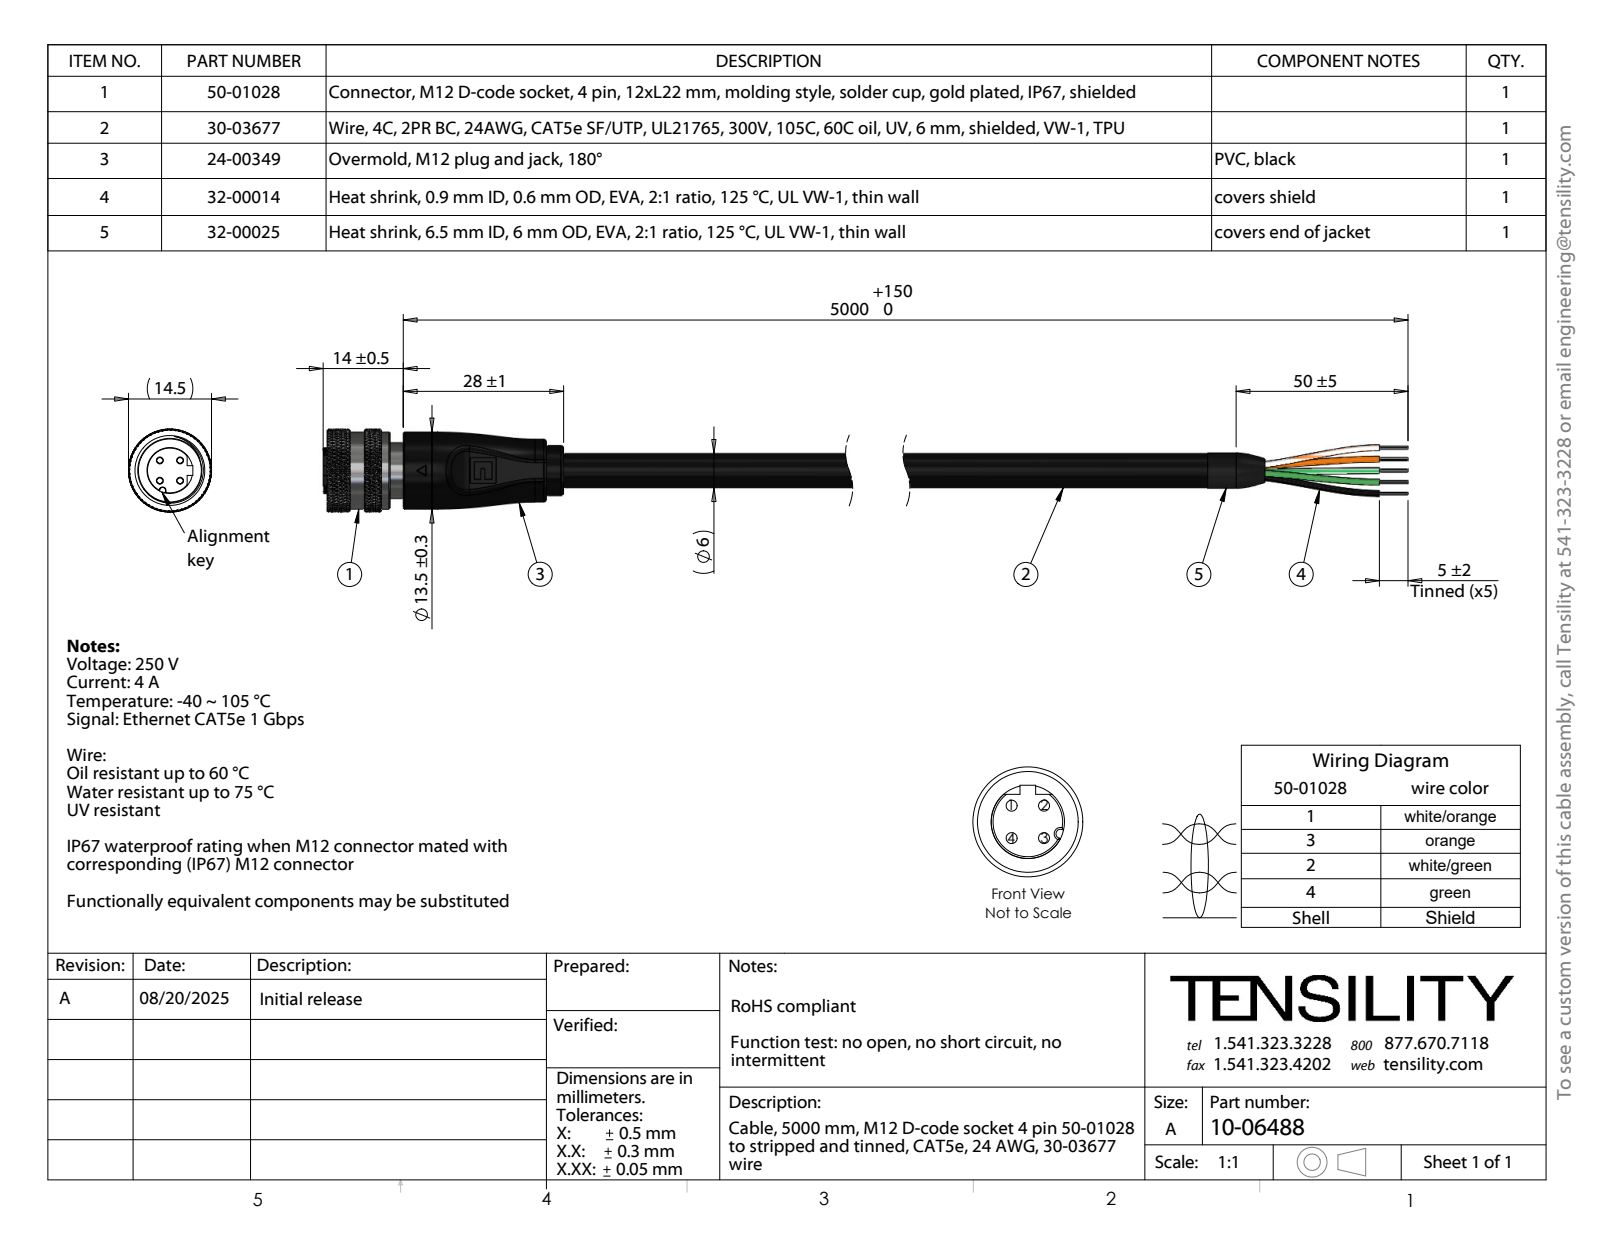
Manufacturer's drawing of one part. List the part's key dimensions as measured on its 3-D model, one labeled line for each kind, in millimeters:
Part name (STEP PRODUCT): 30-03677_s + t; 50-01028_默认; 50-01028-02_默认; 10-06488 (+5 more)
STEP written by: SolidWorks 2025 (CONFIG_CONTROL_DESIGN)
Units: millimetres
Bodies: 87 solids, 3550 faces (339 planar, 940 cylindrical, 2271 other)
Overall size (bounding box): 222 × 14.5 × 14.5
Volume: 9 616 mm³ · Surface area: 27 027 mm²
Round holes (diameter × count): ⌀0.2 ×28, ⌀1.05 ×4, ⌀1.1 ×4, ⌀1.2 ×4, ⌀3.16 ×1, ⌀3.21 ×1, ⌀3.36 ×1, ⌀9 ×1, ⌀10 ×1, ⌀11.2 ×1
Round bosses / shafts (diameter × count): ⌀0.2 ×35, ⌀1.6 ×4, ⌀1.5 ×4, ⌀13.5 ×1, ⌀11 ×1, ⌀10.6 ×1, ⌀10.5 ×1, ⌀9.8 ×1
Partial cylindrical surfaces — rounded edges, fillets, slot ends (radius × count): R0.1 ×10, R0.4 ×6, R0.5 ×2, R1.5 ×2, R4 ×1, R5 ×1, R5.58 ×1, R6.75 ×1
Main face-to-face distances: 178, 28, 150, 7, 4.7, 1, 31.8, 3.5, 23.3, 173.3
Hole centre spacings: 1.91, 0.36, 2.09, 1.06, 0.89, 1.08, 1.24, 1.8
